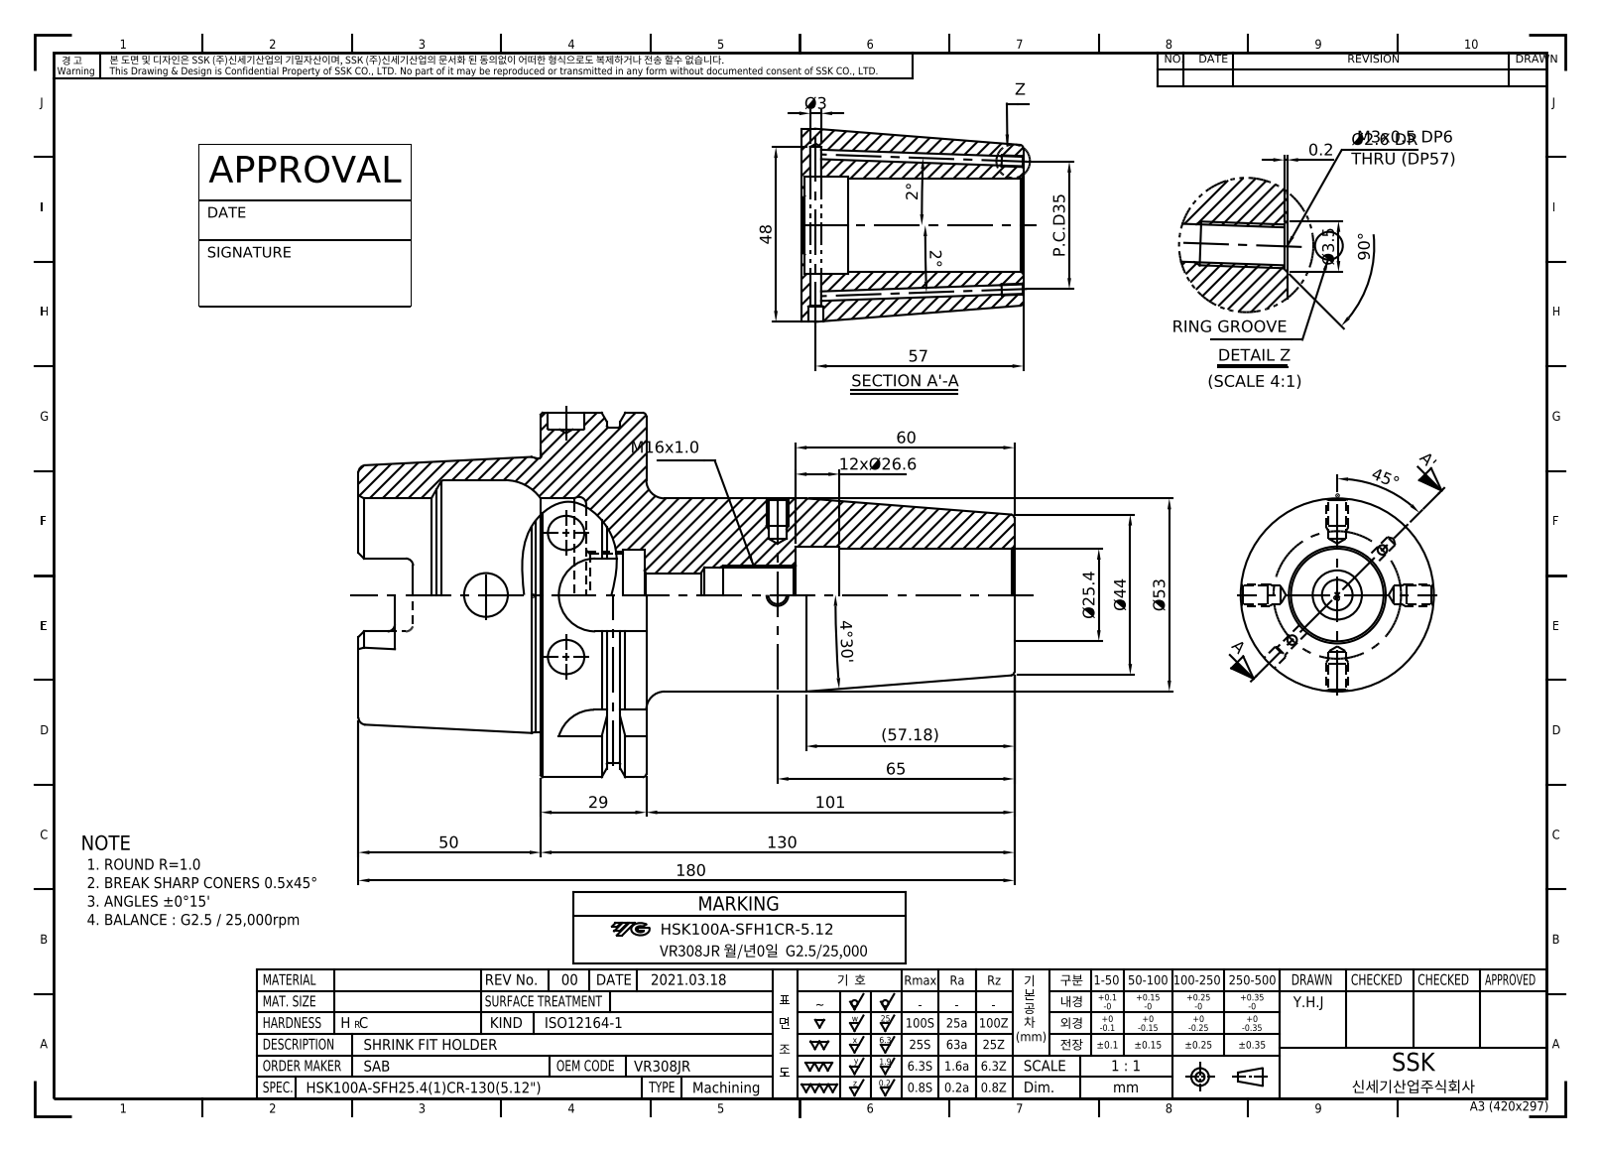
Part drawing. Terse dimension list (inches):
name: LO-HSK100A-SFH25.4CR-130
written by: Autodesk Inventor 2022 (AUTOMOTIVE_DESIGN)
unit: in
bodies: 1 solid, 119 faces (38 planar, 37 cylindrical, 44 other)
size: 7.087 × 3.937 × 3.937
volume: 25.62 in³; area: 111.6 in²
holes: 2× ⌀0.097, 2× ⌀0.472, 1× ⌀0.394, 1× ⌀0.587, 1× ⌀0.881, 1× ⌀0.984, 1× ⌀1, 1× ⌀1.047, 1× ⌀2.087, 1× ⌀2.48
bosses: 1× ⌀3.937, 1× ⌀3.622, 1× ⌀2.969
rounds: 6× R0.079, 4× R0.192, 4× R0.394
face distances: 1.142, 0.492, 0.65, 2.461, 1.969, 3.11, 7.087, 5.118, 4.626, 3.976
